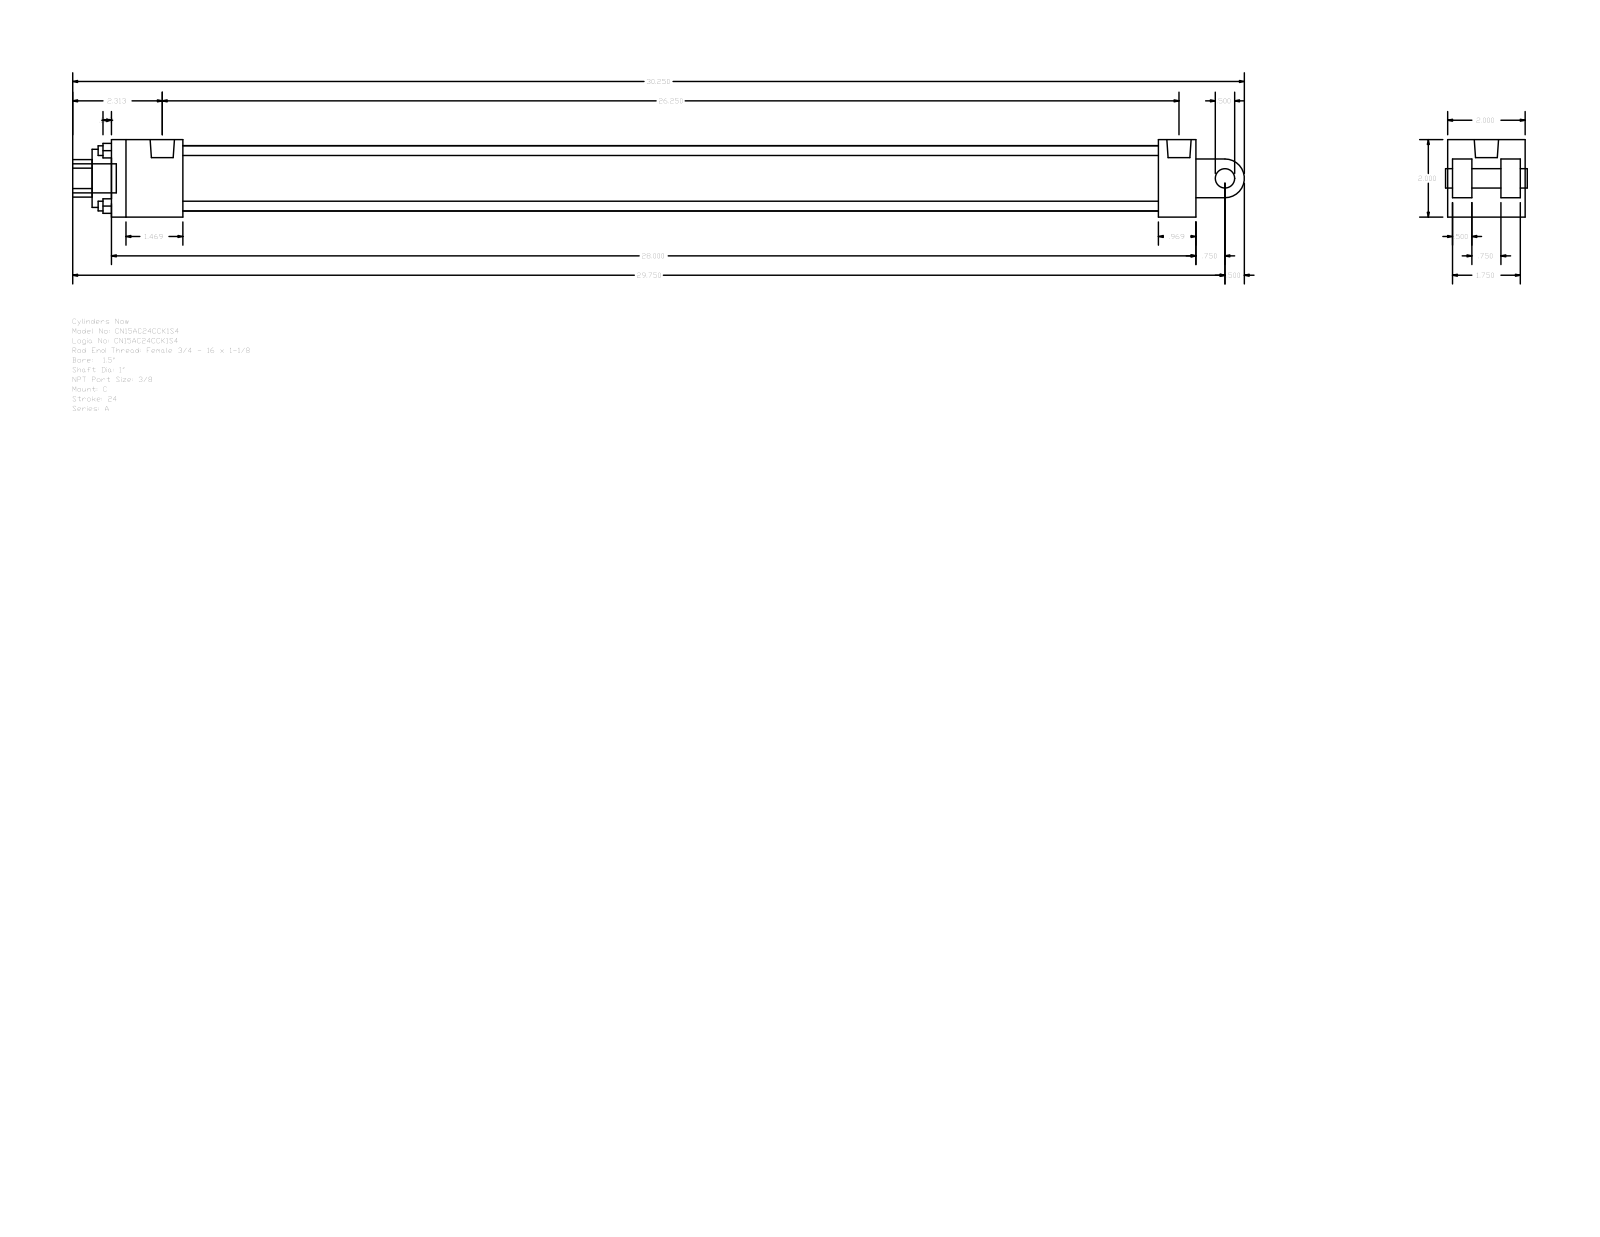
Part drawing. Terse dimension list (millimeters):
name: A_C__0150_1
written by: GSSL Pune (CONFIG_CONTROL_DESIGN)
unit: mm
bodies: 0 solids, 99 faces (70 planar, 29 cylindrical, 0 other)
size: 768.35 × 50.8 × 50.8
holes: 4× ⌀6.35, 2× ⌀5.56, 1× ⌀15.93, 1× ⌀25.4, 1× ⌀38.1, 1× ⌀42.93
bosses: 2× ⌀5.56, 1× ⌀19.05, 1× ⌀15.93, 1× ⌀12.7
rounds: 1× R12.29, 1× R12.7
face distances: 50.8, 12.7, 3.17, 15.87, 47.63, 34.93, 31.76, 711.2, 686.59, 24.61
hole spacings: 25.68, 36.32, 51.36, 3.97
